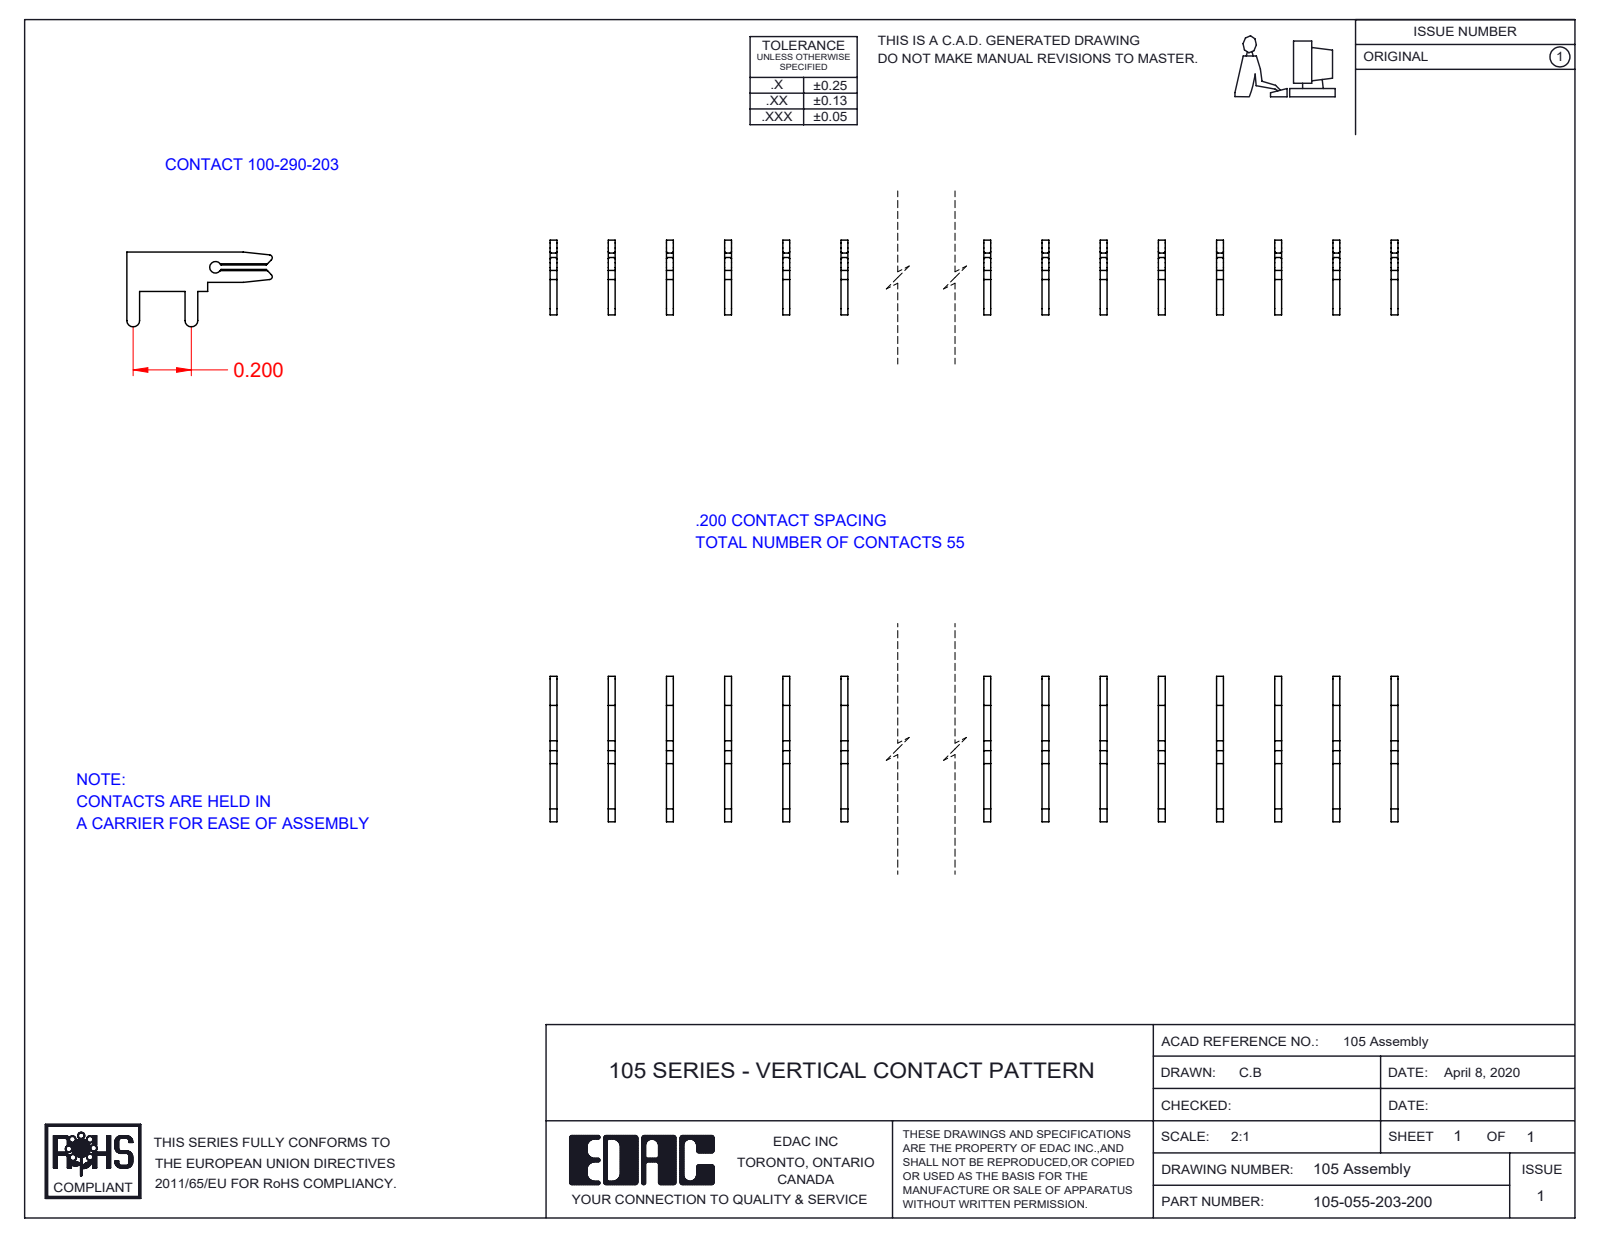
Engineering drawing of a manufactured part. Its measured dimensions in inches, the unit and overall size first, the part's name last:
Units: inches
Overall size (bounding box): 10.824 × 0.5 × 0.257
Round holes (diameter × count): ⌀0.04 ×1
Partial cylindrical surfaces — rounded edges, fillets, slot ends (radius × count): R0.01 ×2, R0.022 ×2
Main face-to-face distances: 0.2, 0.4, 0.6, 0.8, 1, 1.2, 1.4, 1.6, 1.8, 2
Volume: 0.085 in³ · Surface area: 9.865 in²
Bodies: 55 solids, 1540 faces (1155 planar, 385 cylindrical, 0 other)
Part name (STEP PRODUCT): 105-055-203-200; 100-290-001_100-290-203
STEP written by: SolidWorks 2020 (CONFIG_CONTROL_DESIGN)
